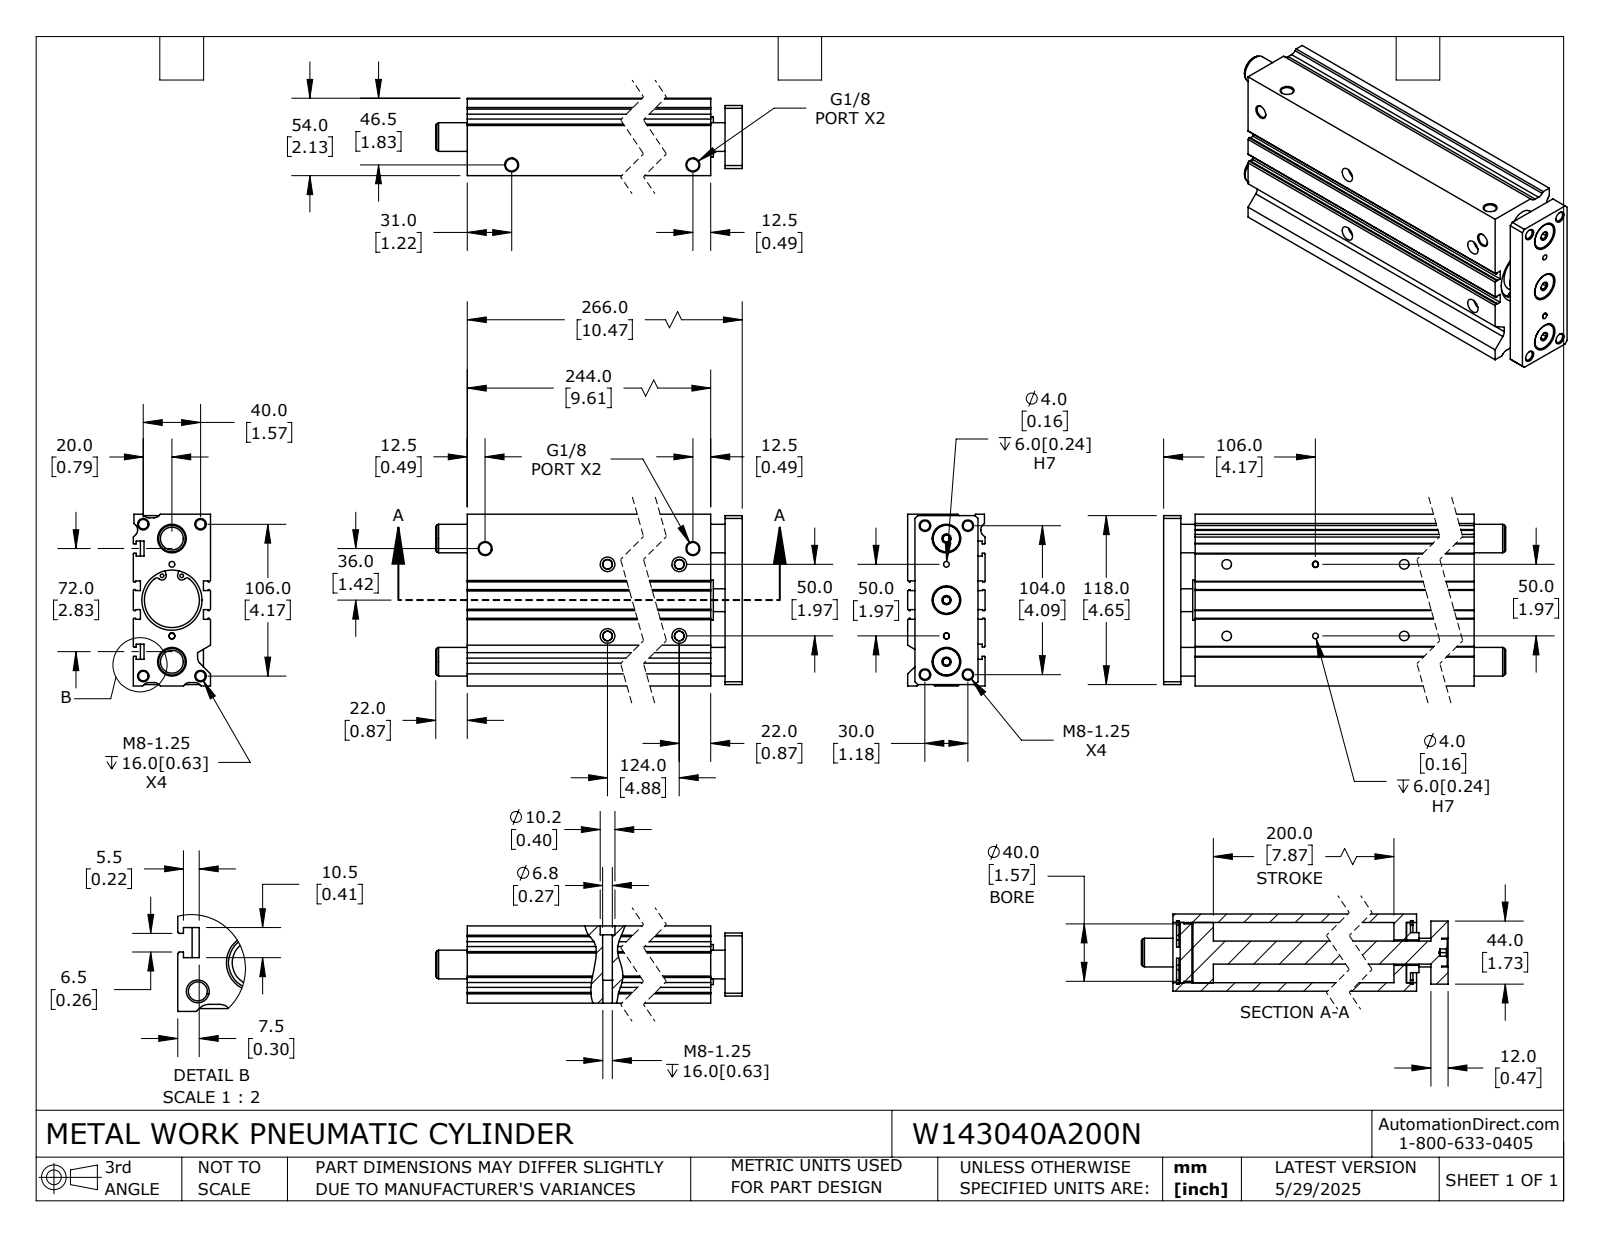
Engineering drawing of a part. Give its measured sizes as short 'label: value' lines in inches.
name: W143040A200N; W143040A200N_BODY; W143040A200N_ROD
written by: SolidWorks 2024 (CONFIG_CONTROL_DESIGN)
unit: in
bodies: 6 solids, 393 faces (192 planar, 151 cylindrical, 50 other)
size: 11.339 × 4.724 × 2.126
volume: 78.48 in³; area: 415.2 in²
holes: 12× ⌀0.262, 4× ⌀0.098, 4× ⌀0.157, 4× ⌀0.268, 4× ⌀0.337, 4× ⌀0.402, 3× ⌀0.197, 3× ⌀0.787, 1× ⌀0.697, 1× ⌀1.51
bosses: 3× ⌀0.748, 2× ⌀1.752, 1× ⌀1.654, 1× ⌀1.575, 1× ⌀1.102, 1× ⌀0.63
rounds: 7× R0.197, 4× R0.079, 4× R0.089, 4× R0.116, 2× R0.157
face distances: 2.126, 0.197, 1.929, 0.098, 4.724, 0.295, 1.831, 1.634, 1.732, 0.866
hole spacings: 0.201, 0.415, 0.689, 0.722, 0.88, 1.059, 1.216, 1.355
